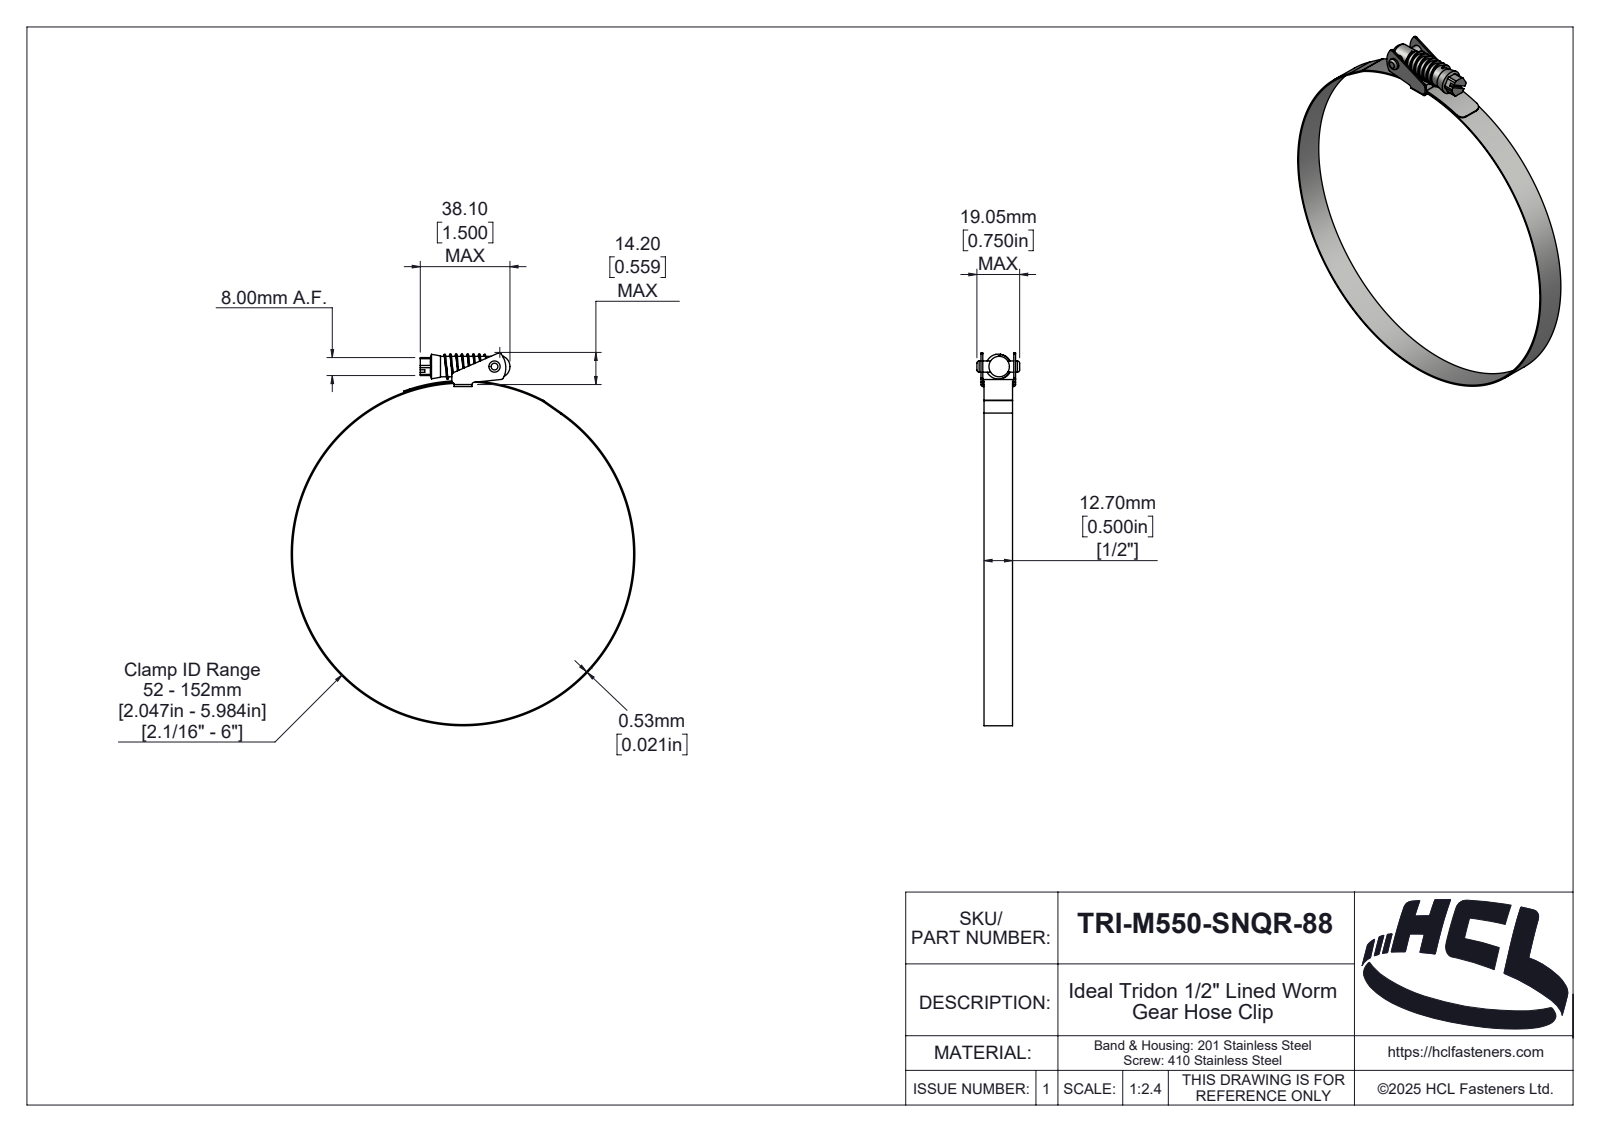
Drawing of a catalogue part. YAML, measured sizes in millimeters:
part_name: "TRI-M550-SNQR-88"
step_written_by: "SolidWorks 2025 (AUTOMOTIVE_DESIGN)"
units: millimeters
bodies: {solids: 5, faces: 222, planar: 44, cylindrical: 112, other: 66}
overall_size: [166.02, 153.06, 19.05]
volume: 6586
surface_area: 16981
round_holes:
  - {diameter: 5, count: 1}
  - {diameter: 152, count: 1}
round_bosses_or_shafts:
  - {diameter: 153.06, count: 1}
  - {diameter: 9.1, count: 1}
partial_cylinders:
  - {radius: 1, count: 11}
  - {radius: 0.1, count: 2}
  - {radius: 0.9, count: 2}
  - {radius: 3, count: 2}
  - {radius: 0.46, count: 1}
  - {radius: 1.89, count: 1}
  - {radius: 2, count: 1}
  - {radius: 2.35, count: 1}
face_to_face_distances: [0.8, 1.35, 14.05, 14.6, 0.55, 13.25, 12.7, 15.4, 13.8, 0.53]
hole_center_spacings: [84.57]
